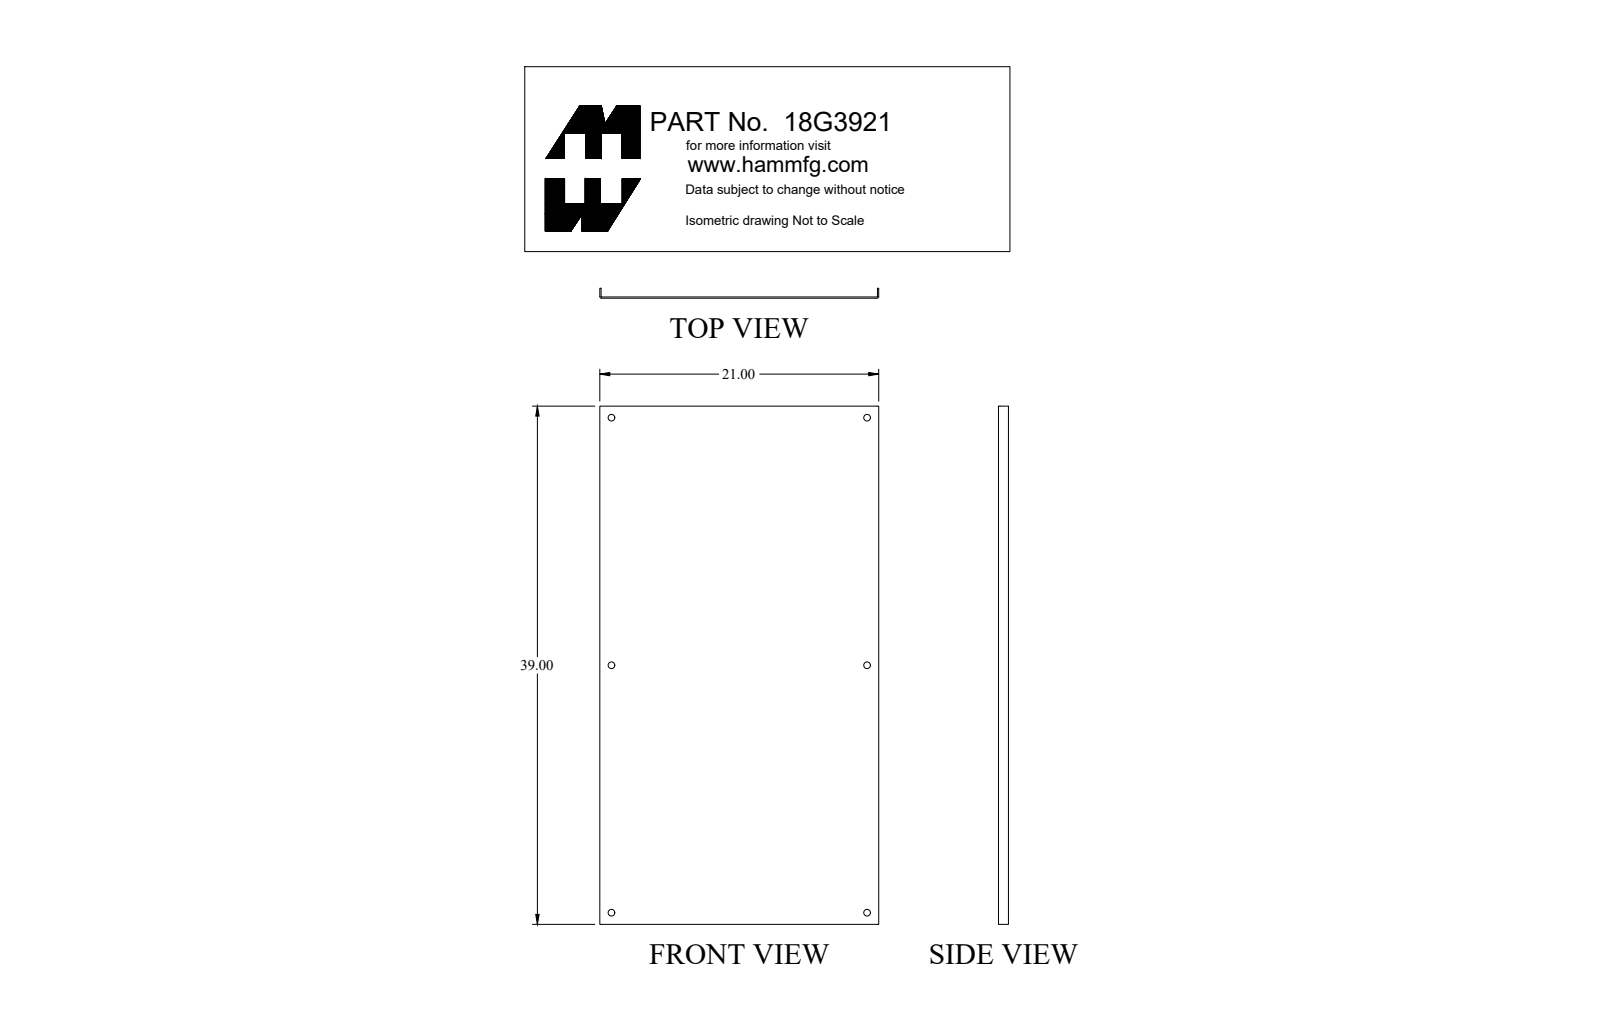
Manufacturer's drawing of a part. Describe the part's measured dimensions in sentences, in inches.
The part is named "18G3921_Default". Its 3-D file was written by "SolidWorks 2018 (CONFIG_CONTROL_DESIGN)". It is 1 solid with 26 faces: 10 planar, 16 cylindrical and 0 other. Overall it measures 39 by 21 by 0.75 inches. Its volume is 82.3 cubic inches and its surface area 1 745 square inches. Round holes: 6 of diameter 0.5. Partial cylindrical surfaces (rounded edges, fillets, slot ends): 2 of radius 0.03, 2 of radius 0.125. The main face-to-face distances are 0.095, 20.905, 20.81, 21, 0.75, 0.655, 39. The hole center spacings are 18.625, 26.785, 19.25, 37.25, 41.93.
